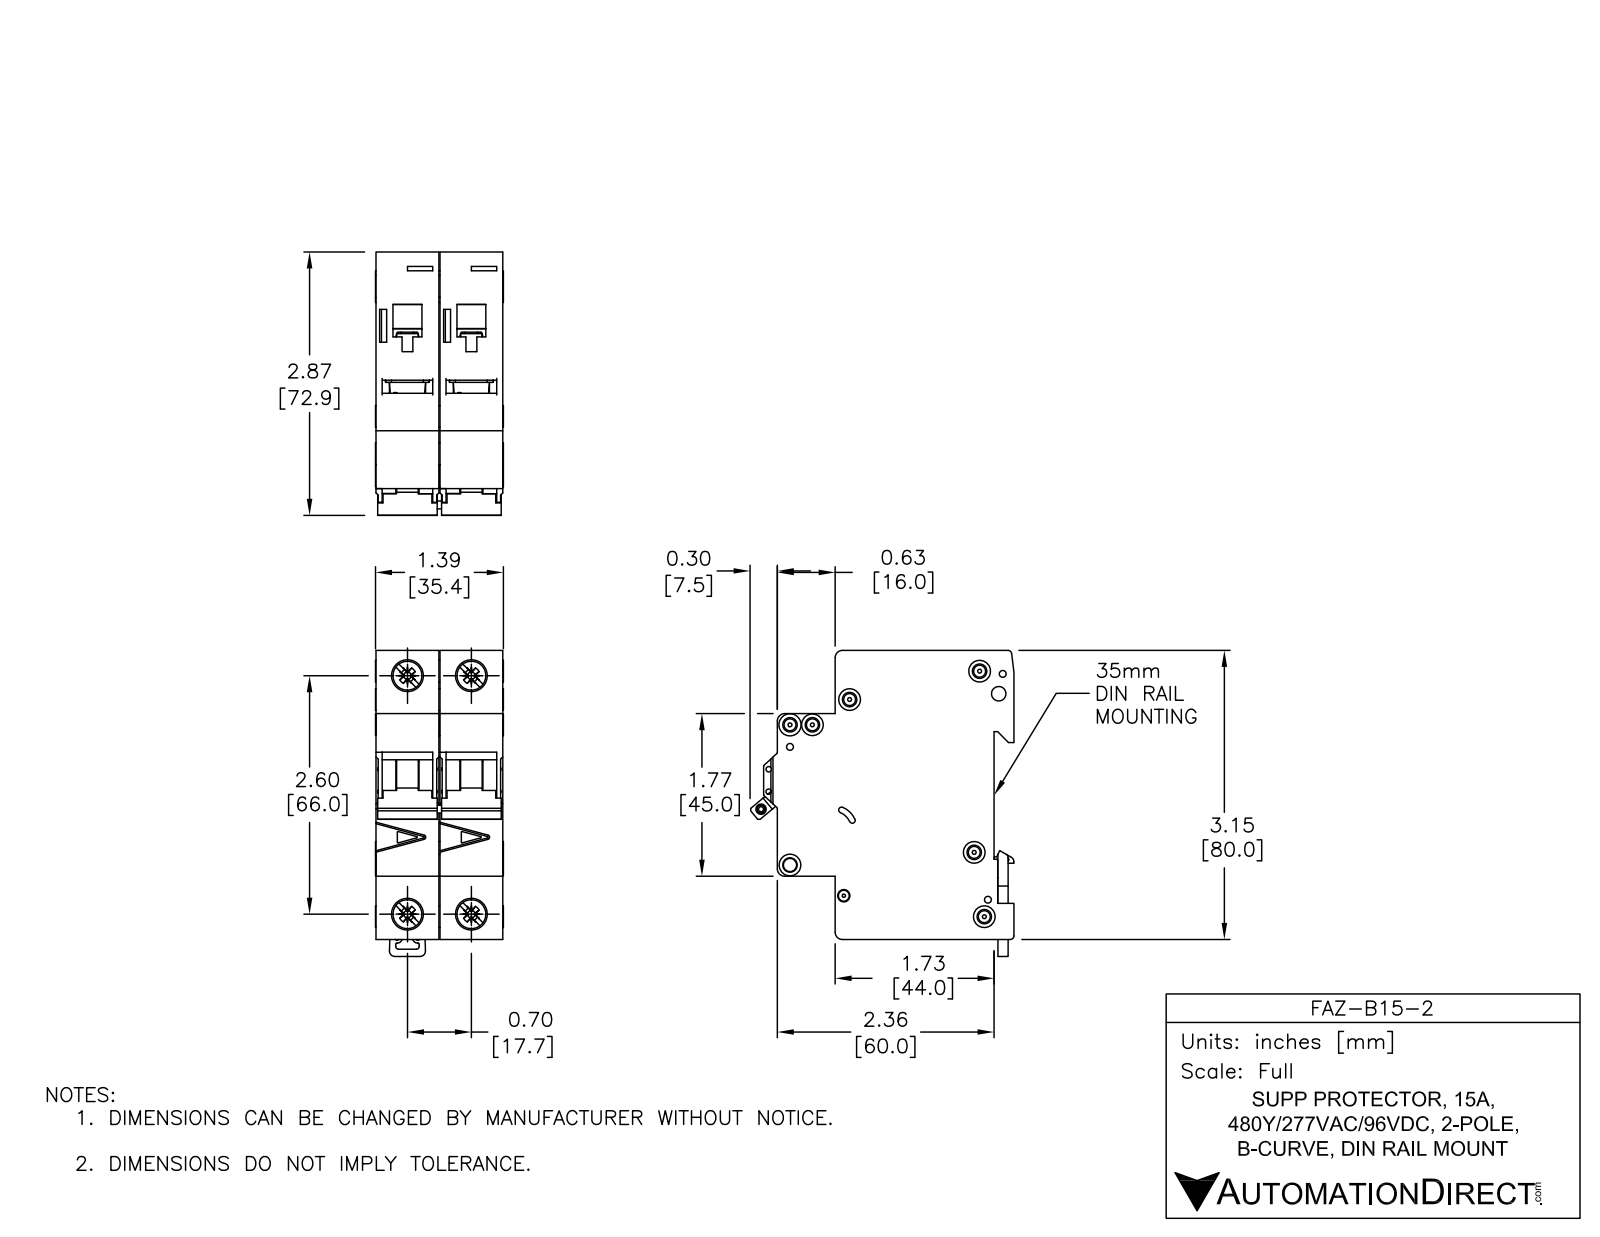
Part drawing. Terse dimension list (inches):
name: FAZ-B15-2
written by: SolidWorks 2014 (AUTOMOTIVE_DESIGN)
unit: in
bodies: 8 solids, 1104 faces (466 planar, 396 cylindrical, 242 other)
size: 3.338 × 2.876 × 1.394
volume: 9.142 in³; area: 60.14 in²
holes: 6× ⌀0.142, 3× ⌀0.075, 2× ⌀0.043, 2× ⌀0.059, 2× ⌀0.157, 2× ⌀0.281, 2× ⌀0.323, 1× ⌀0.085, 1× ⌀0.087, 1× ⌀0.1, 1× ⌀0.13, 1× ⌀0.134
bosses: 4× ⌀0.236, 2× ⌀0.323, 2× ⌀0.098
rounds: 49× R0.01, 19× R0.02, 10× R0.079, 8× R0.008, 8× R0.039, 2× R0.031, 2× R0.071, 2× R0.118
face distances: 0.697, 0.689, 1.386, 3.129, 0.217, 1.949, 1.732, 2.579, 2.362, 0.63
hole spacings: 0.244, 0.537, 0.697, 2.598, 2.69, 0.189, 0.204, 0.221
